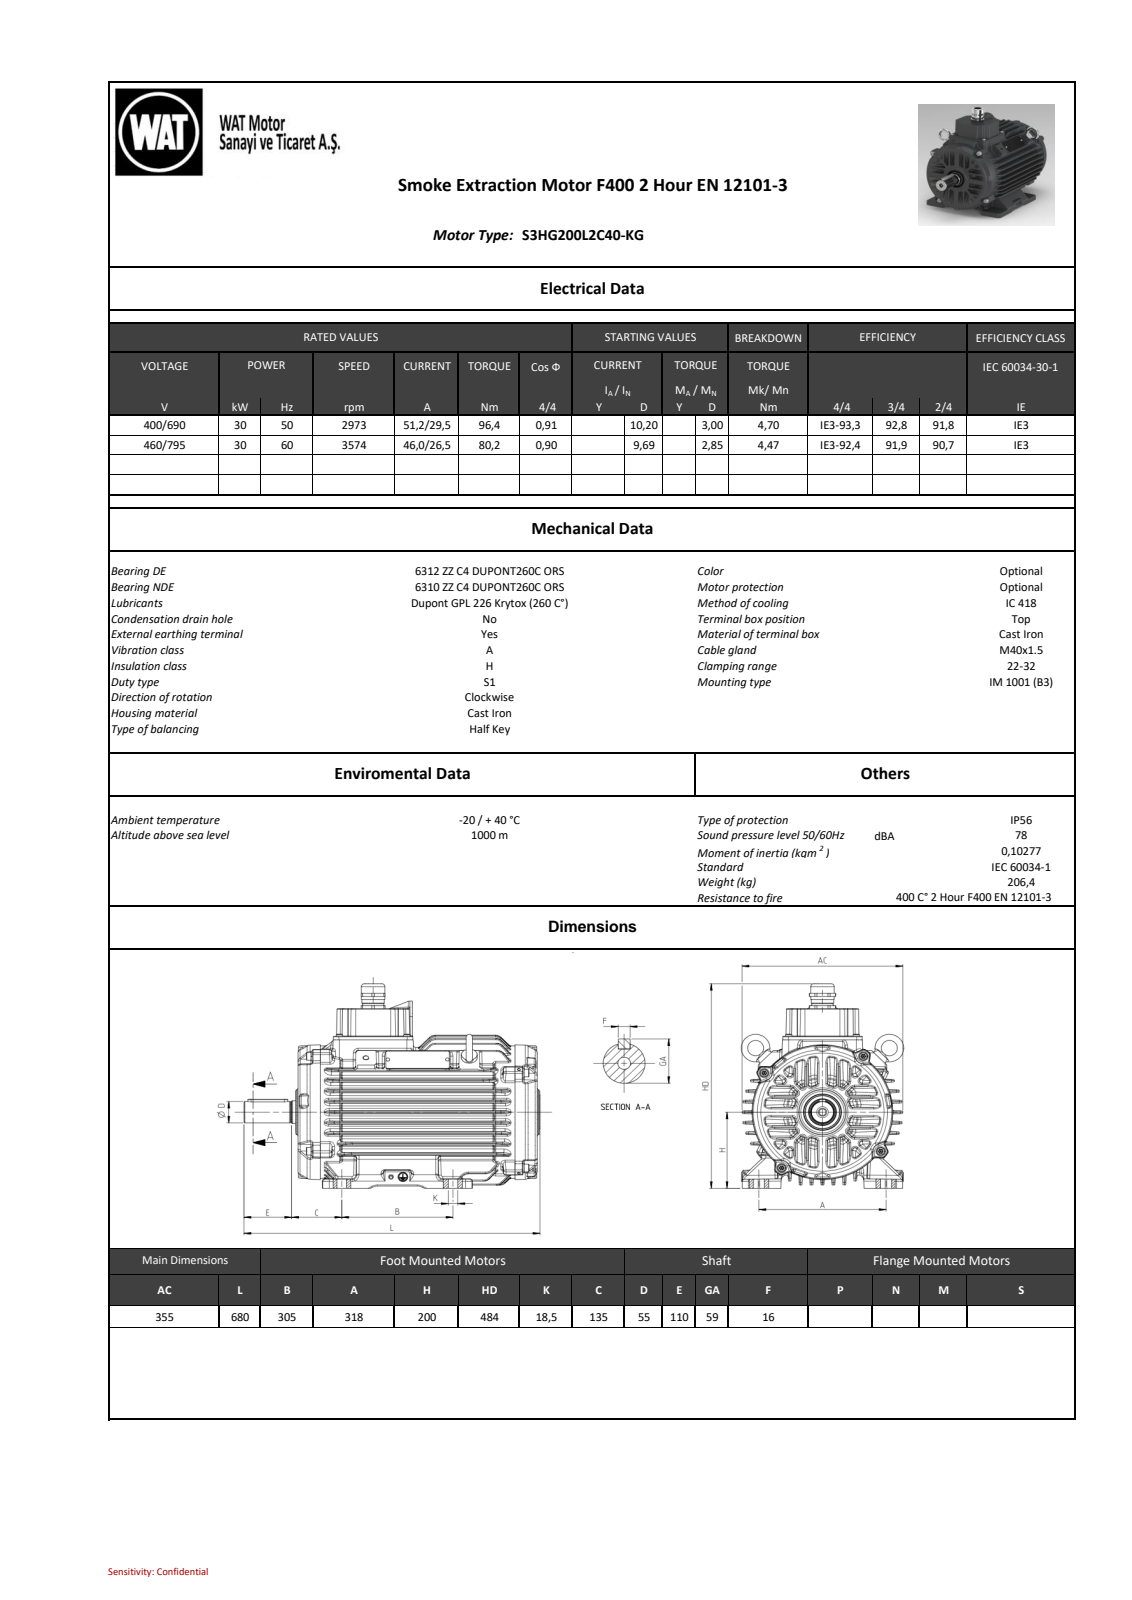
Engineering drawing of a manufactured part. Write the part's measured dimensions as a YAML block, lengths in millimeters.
part_name: "260381480CFDz3ku"
step_written_by: "SIEMENS PLM Software NX 11.0 (AUTOMOTIVE_DESIGN)"
units: millimeters
bodies: {solids: 0, faces: 6861, planar: 923, cylindrical: 1596, other: 4342}
overall_size: [680, 484, 391]
round_holes:
  - {diameter: 10.3, count: 8}
  - {diameter: 5, count: 5}
  - {diameter: 2.5, count: 2}
  - {diameter: 14, count: 2}
  - {diameter: 17.5, count: 1}
  - {diameter: 21, count: 1}
  - {diameter: 32, count: 1}
  - {diameter: 62, count: 1}
round_bosses_or_shafts:
  - {diameter: 20, count: 4}
  - {diameter: 16, count: 4}
  - {diameter: 15.73, count: 4}
  - {diameter: 12, count: 4}
  - {diameter: 18.1, count: 3}
  - {diameter: 35, count: 2}
  - {diameter: 310, count: 1}
  - {diameter: 88.89, count: 1}
partial_cylinders:
  - {radius: 4, count: 399}
  - {radius: 3, count: 177}
  - {radius: 1.5, count: 136}
  - {radius: 2, count: 87}
  - {radius: 5, count: 65}
  - {radius: 1.8, count: 64}
  - {radius: 1, count: 26}
  - {radius: 0.4, count: 22}
face_to_face_distances: [14.54, 14.46, 29, 29.14, 14.6, 43.6, 58.71, 43.79, 29.25, 14.65]
hole_center_spacings: [158.01, 223.45, 54.87, 181.26, 258.86, 311.21, 316.01, 75]
